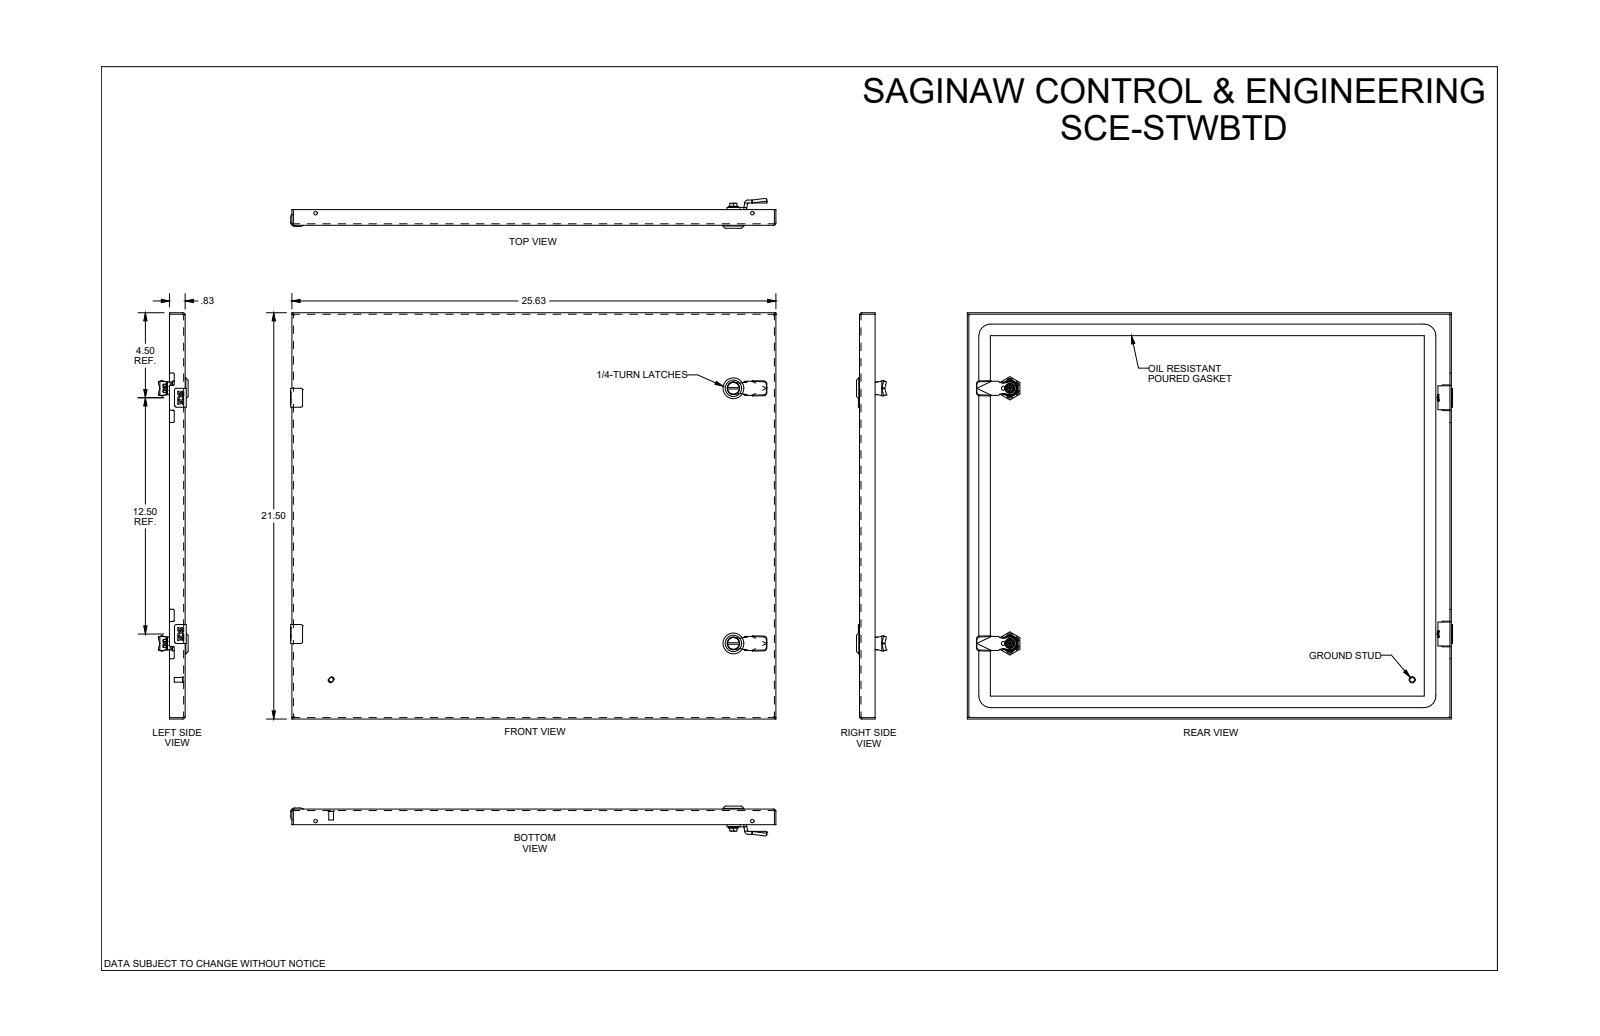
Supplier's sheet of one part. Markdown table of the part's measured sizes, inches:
| quantity | value |
| --- | --- |
| part name | SCE-STWBTD |
| STEP written by | SolidWorks 2019 (AUTOMOTIVE_DESIGN) |
| units | inches |
| bodies | 29 solids, 1611 faces (784 planar, 579 cylindrical, 248 other) |
| overall size | 25.685 × 21.5 × 1.573 |
| volume | 54.32 in³ |
| surface area | 1 461 in² |
| round holes (diameter × count) | 0.172 × 4, 0.205 × 4, 0.244 × 4, 0.375 × 4, 0.04 × 2, 0.156 × 2, 0.188 × 2, 0.197 × 2, 0.218 × 2, 0.315 × 2, 0.394 × 2, 0.634 × 2 |
| round bosses / shafts (diameter × count) | 0.17 × 6, 0.25 × 4, 0.24 × 4, 0.196 × 3, 1.102 × 2, 0.78 × 2, 0.63 × 2, 0.531 × 2 |
| partial cylindrical surfaces (radius × count) | 0.012 × 56, 0.015 × 24, 0.02 × 20, 0.031 × 9, 0.06 × 9, 0.025 × 8, 0.062 × 8, 0.1 × 8 |
| main face-to-face distances | 0.06, 0.078, 0.018, 21.44, 25.565, 21.5, 21.38, 25.625, 25.506, 0.28 |
| hole center spacings | 12.5, 0.494, 0.984, 12.008, 12.992, 22.664, 22.685, 22.709 |
